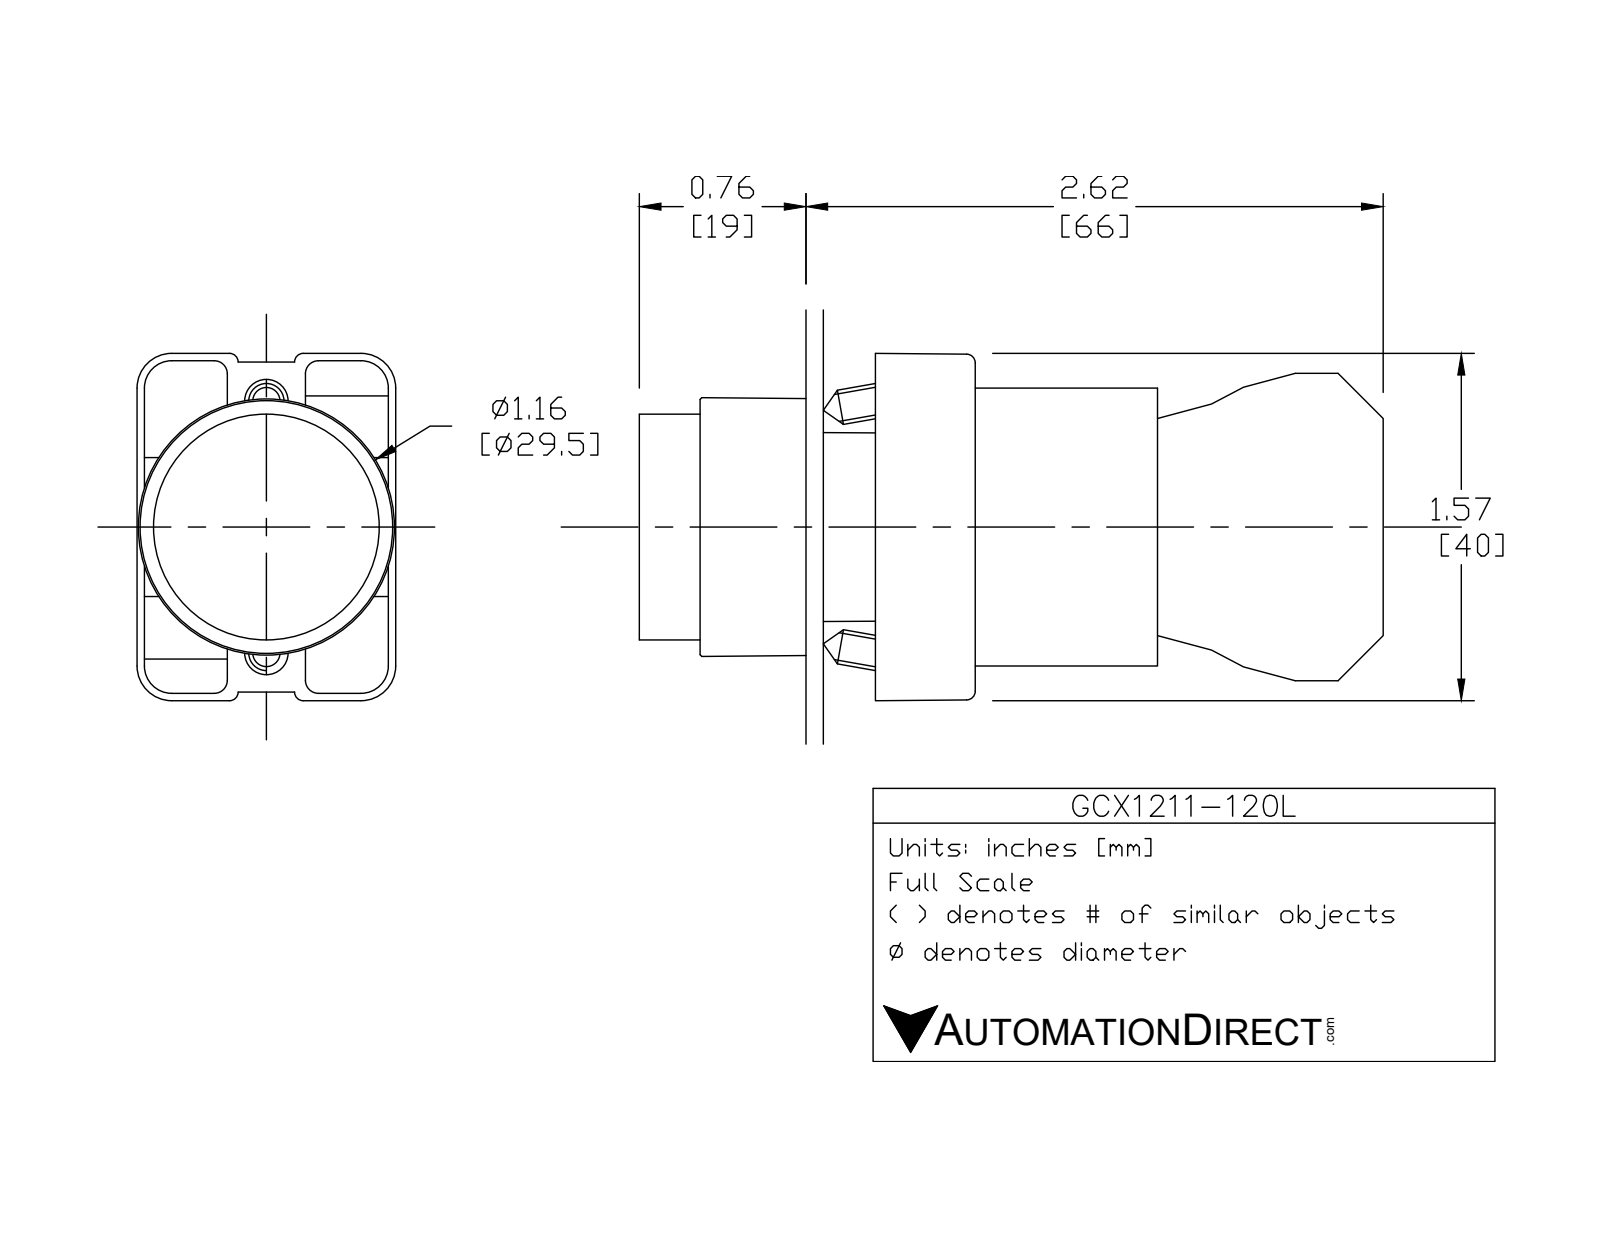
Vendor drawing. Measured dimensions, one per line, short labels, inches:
name: ecx1030; ecx1029; GCX1211L OPERATOR; GCX1211-120L (+1 more)
written by: SolidWorks 2016 (AUTOMOTIVE_DESIGN)
unit: in
bodies: 7 solids, 425 faces (250 planar, 144 cylindrical, 31 other)
size: 3.319 × 1.581 × 1.177
volume: 2.721 in³; area: 36.32 in²
holes: 2× ⌀0.079, 2× ⌀0.124, 2× ⌀0.13, 1× ⌀0.087, 1× ⌀0.197, 1× ⌀0.469, 1× ⌀0.878, 1× ⌀0.888, 1× ⌀1.024
bosses: 4× ⌀0.157, 1× ⌀1.175, 1× ⌀1.004, 1× ⌀0.945, 1× ⌀0.856, 1× ⌀0.78, 1× ⌀0.504
rounds: 24× R0.059, 12× R0.041, 12× R0.124, 12× R0.157, 8× R0.039, 2× R0.128, 1× R0.02, 1× R0.063
face distances: 0.827, 0.579, 1.171, 2.02, 1.193, 0.031, 0.033, 0.573, 1.165, 0.593
hole spacings: 0.236, 0.544, 0.472, 0.49
